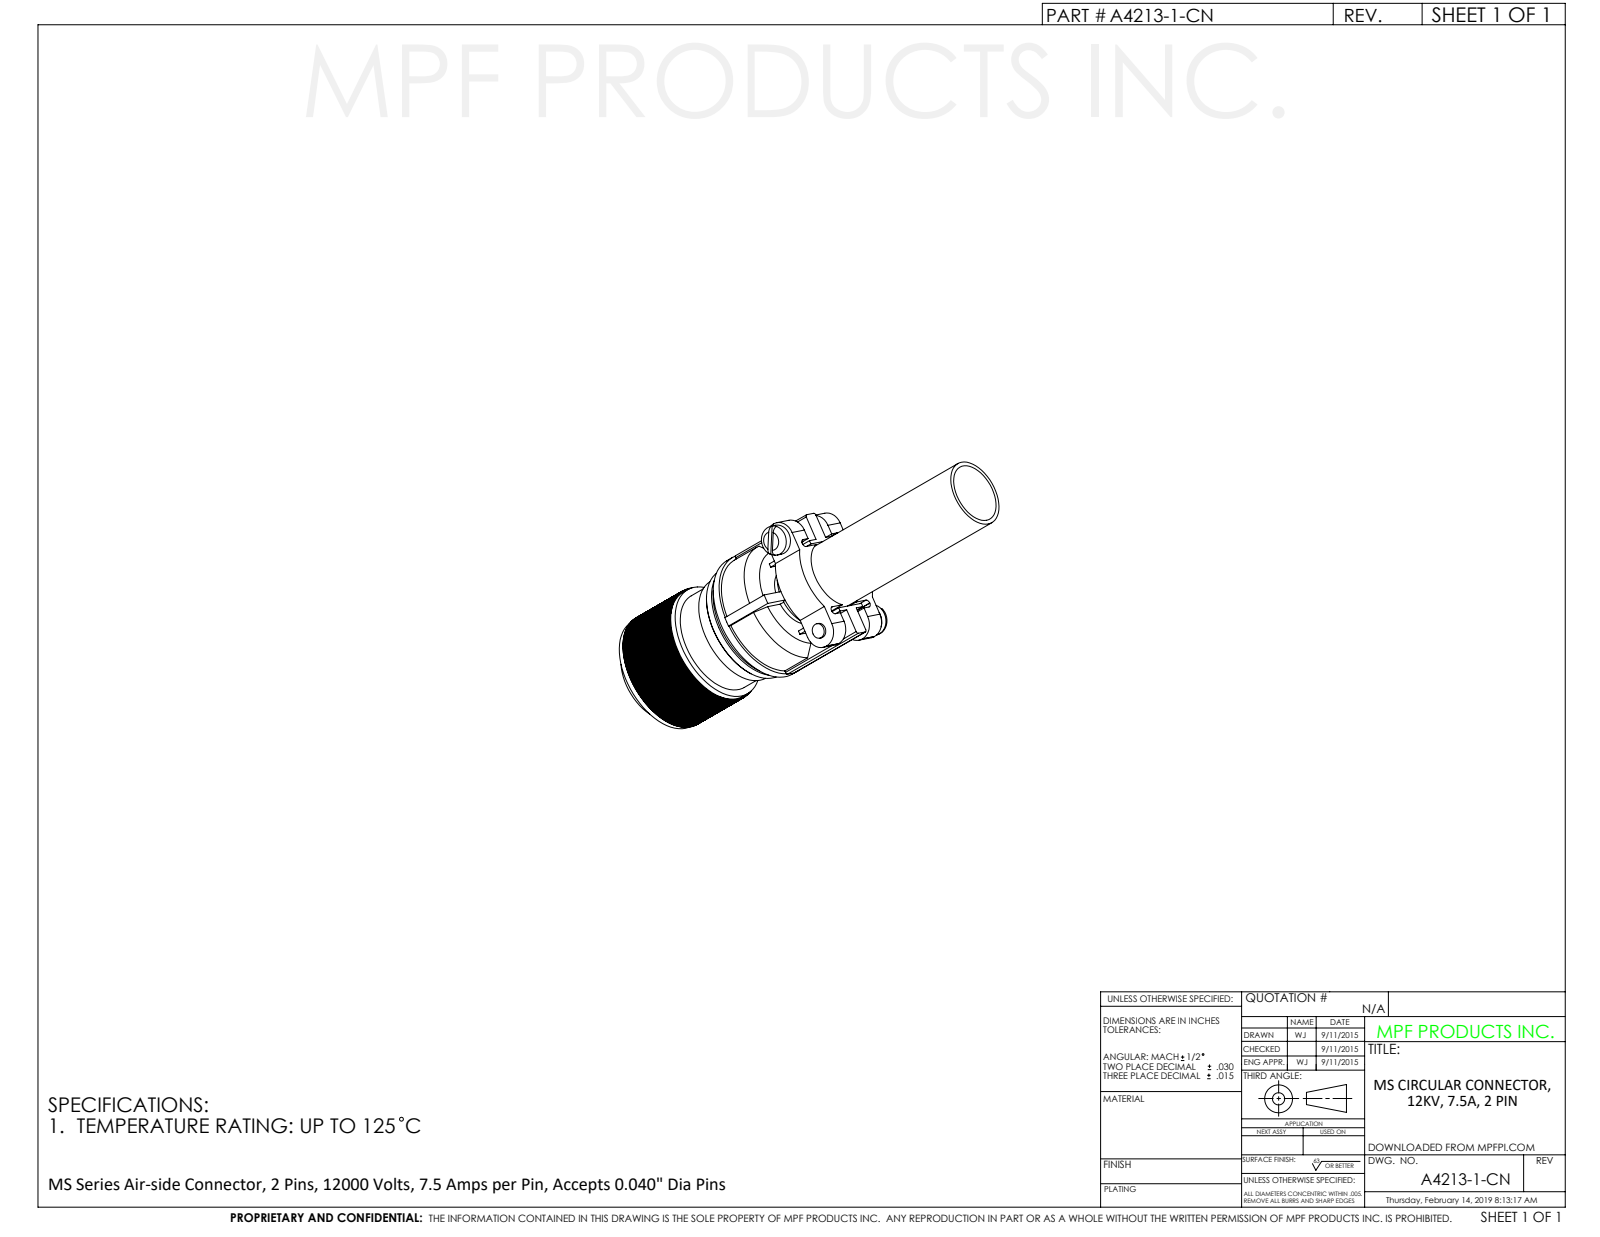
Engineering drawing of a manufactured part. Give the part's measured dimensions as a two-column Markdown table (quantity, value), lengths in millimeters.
| quantity | value |
| --- | --- |
| part name | A4213-1-CN; MID RING 2; A4219; A4216_A4216-2 (+2 more) |
| STEP written by | SolidWorks 2012 (CONFIG_CONTROL_DESIGN) |
| units | millimeters |
| bodies | 5 solids, 797 faces (149 planar, 287 cylindrical, 361 other) |
| overall size | 106.4 × 37.7 × 36.7 |
| volume | 30 200 mm³ |
| surface area | 29 920 mm² |
| round holes (diameter × count) | 0.8 × 2, 1.1 × 2, 1.2 × 2, 1.4 × 2, 1.7 × 2, 2.5 × 2, 3 × 2, 3.9 × 2, 0.3 × 1, 14 × 1, 16.8 × 1, 18.2 × 1 |
| round bosses / shafts (diameter × count) | 3.4 × 2, 3 × 2, 2.5 × 2, 2 × 2, 2 × 2, 1.3 × 2, 30.5 × 1, 29 × 1 |
| partial cylindrical surfaces (radius × count) | 0.9 × 8, 4 × 5, 0.5 × 4, 8.2 × 1, 12 × 1, 12 × 1 |
| main face-to-face distances | 7.1, 6.7, 13.8, 24.1, 17.4, 10.3, 23.3, 16.6, 9.5, 0.8 |
| hole center spacings | 5.2, 8.6, 10.3 |
